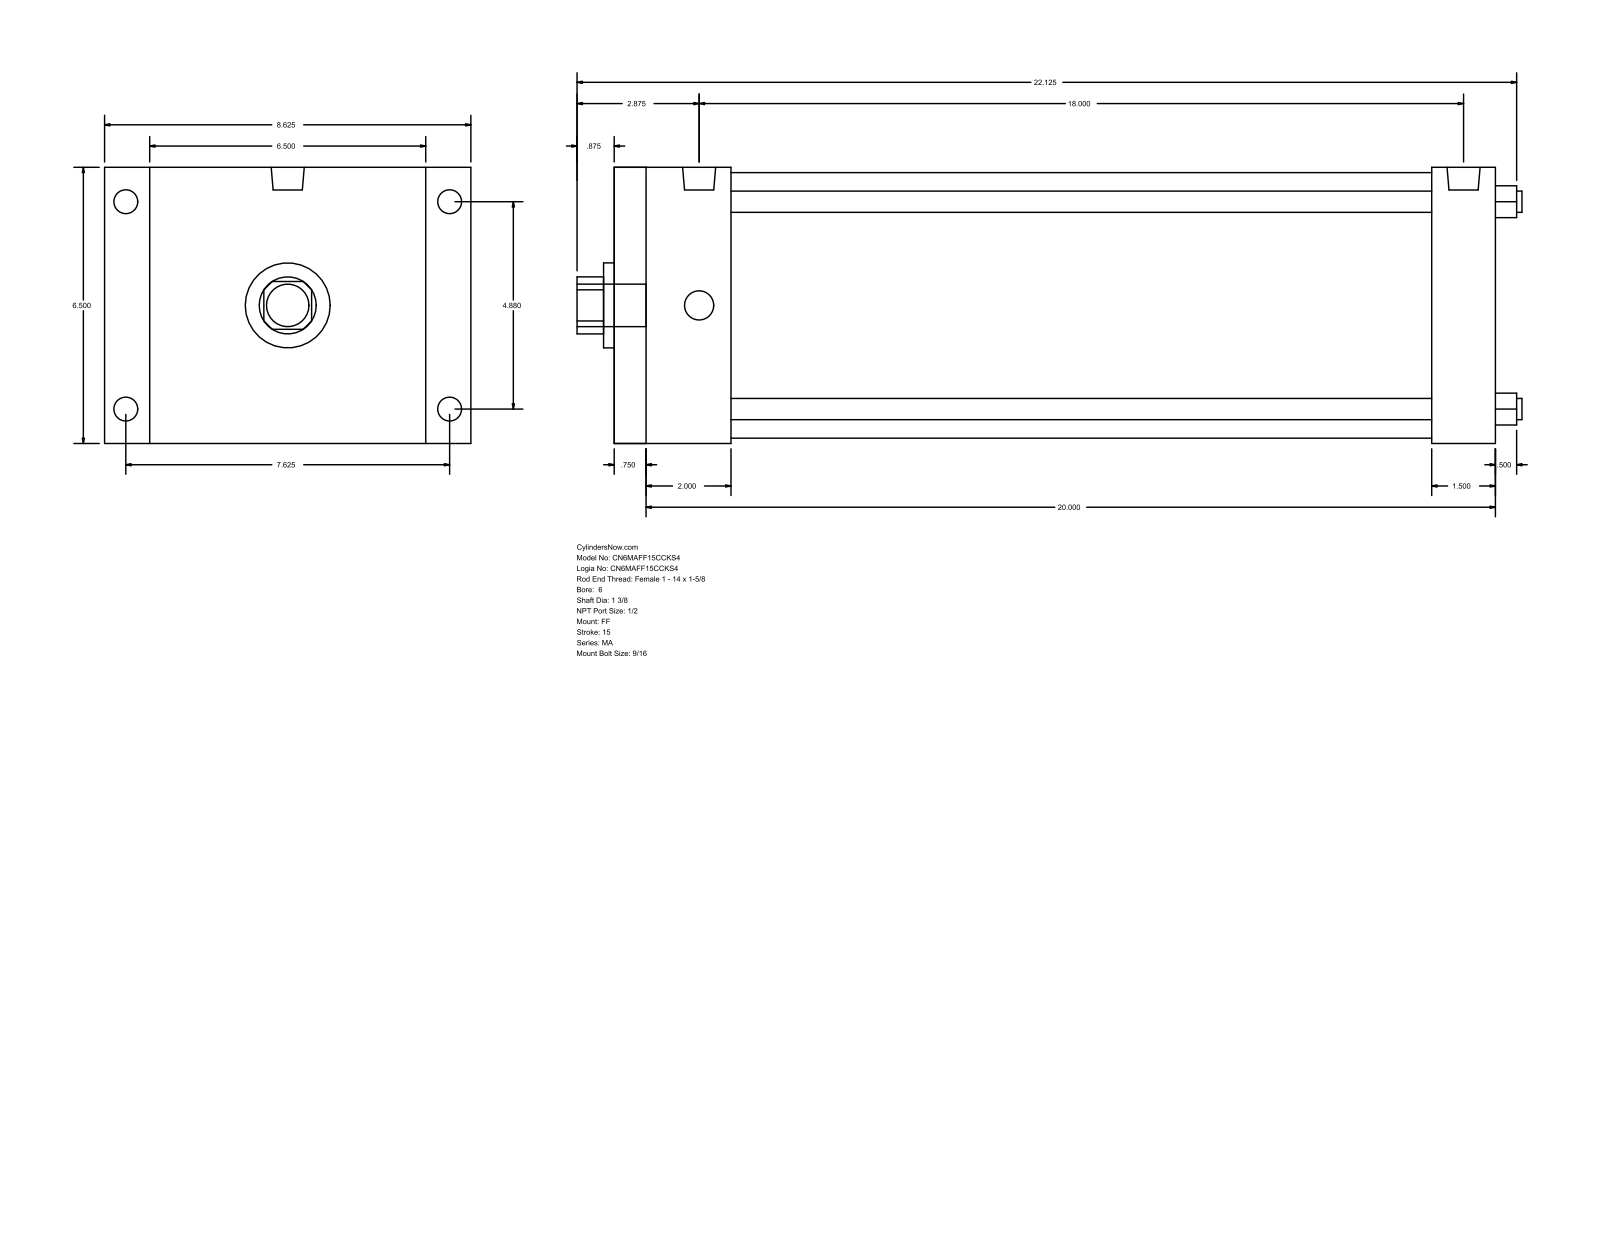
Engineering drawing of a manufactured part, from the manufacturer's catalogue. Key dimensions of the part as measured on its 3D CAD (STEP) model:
Part name (STEP PRODUCT): MA_FF__0600_1.375
STEP written by: GSSL Pune (CONFIG_CONTROL_DESIGN)
Units: millimetres
Bodies: 0 solids, 92 faces (64 planar, 28 cylindrical, 0 other)
Overall size (bounding box): 565.15 × 219.07 × 165.1
Round holes (diameter × count): ⌀12.7 ×4, ⌀34.92 ×1, ⌀50.8 ×1, ⌀158.75 ×1
Round bosses / shafts (diameter × count): ⌀17.46 ×4, ⌀14.29 ×4, ⌀19.77 ×2, ⌀25.4 ×1
Partial cylindrical surfaces — rounded edges, fillets, slot ends (radius × count): R17.06 ×1
Main face-to-face distances: 165.1, 527.04, 15.87, 511.17, 50.8, 473.08, 66.67, 460.37, 488.95, 422.28
Hole centre spacings: 87.65, 123.96, 175.31
